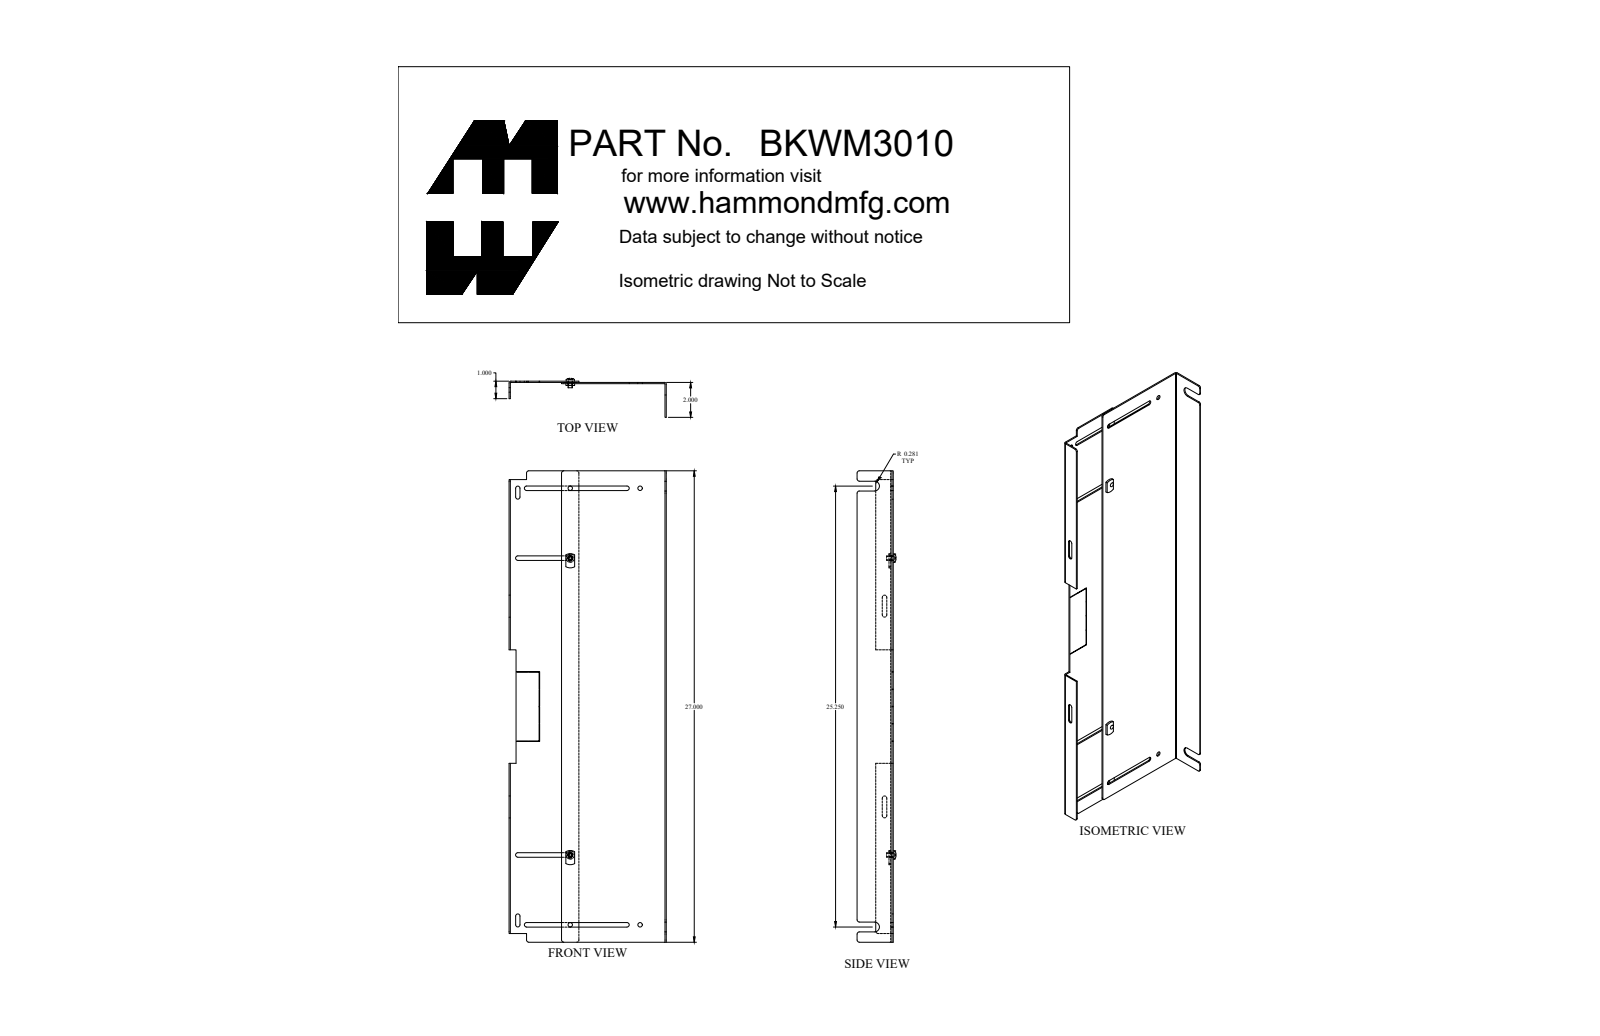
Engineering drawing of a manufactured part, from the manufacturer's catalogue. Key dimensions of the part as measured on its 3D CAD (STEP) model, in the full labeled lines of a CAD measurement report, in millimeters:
Part name (STEP PRODUCT): BKWM3010_Default
STEP written by: SolidWorks 2019 (CONFIG_CONTROL_DESIGN)
Units: millimetres
Bodies: 6 solids, 216 faces (116 planar, 78 cylindrical, 22 other)
Overall size (bounding box): 685.8 × 228.7 × 56.8
Volume: 388 700 mm³ · Surface area: 434 500 mm²
Round holes (diameter × count): ⌀5.1 ×2, ⌀6.6 ×2, ⌀8 ×2
Round bosses / shafts (diameter × count): ⌀11.9 ×2, ⌀7.4 ×2, ⌀6.4 ×2
Partial cylindrical surfaces — rounded edges, fillets, slot ends (radius × count): R3.2 ×18, R3.3 ×16, R12.7 ×4, R0.9 ×2, R2.7 ×2, R7.1 ×2
Main face-to-face distances: 1.8, 3.7, 226.9, 225.1, 228.7, 101.6, 76.3, 74.5, 150.6, 152.4
Hole centre spacings: 143.7, 543, 431.8, 635
